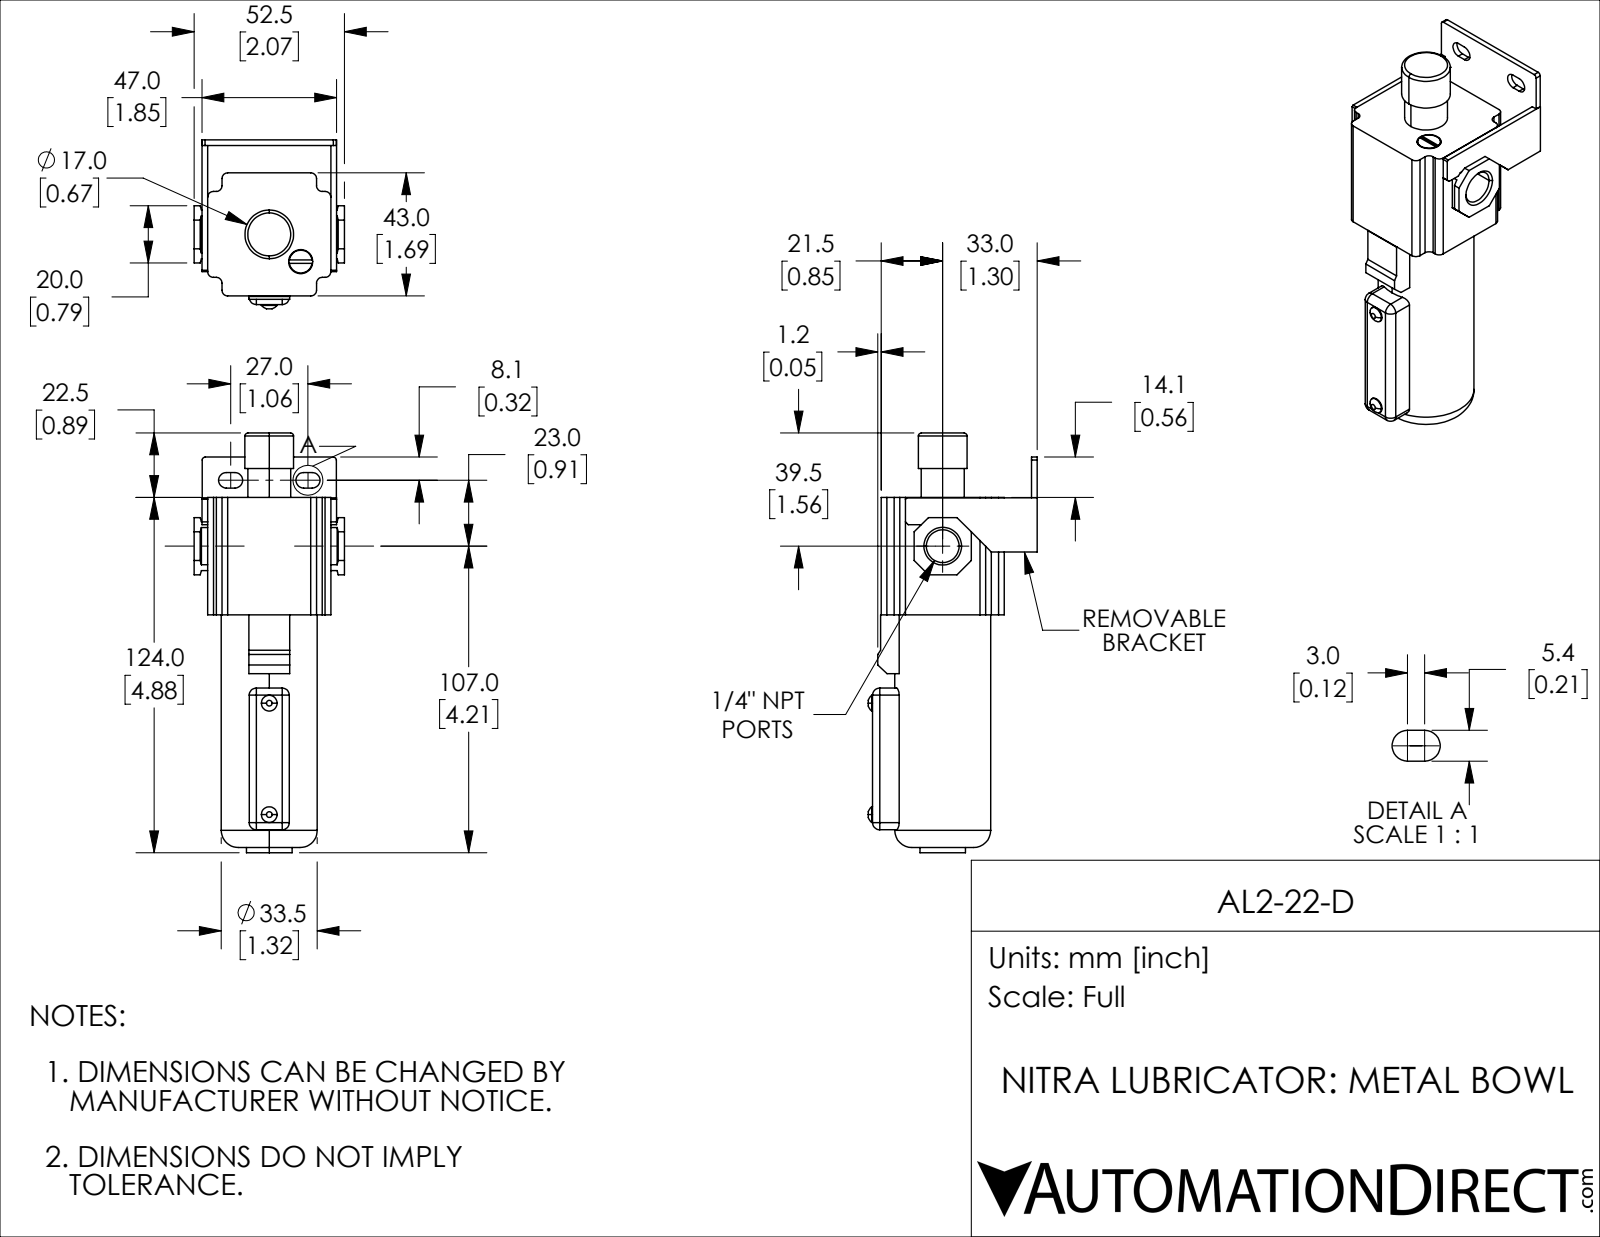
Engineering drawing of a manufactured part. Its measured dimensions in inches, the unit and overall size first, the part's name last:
Units: inches
Overall size (bounding box): 5.768 × 2.323 × 2.067
Round holes (diameter × count): ⌀0.331 ×1, ⌀0.451 ×1
Round bosses / shafts (diameter × count): ⌀0.217 ×2, ⌀1.319 ×1, ⌀0.669 ×1, ⌀0.626 ×1, ⌀0.591 ×1, ⌀0.315 ×1
Partial cylindrical surfaces — rounded edges, fillets, slot ends (radius × count): R0.079 ×12, R0.098 ×8, R0.106 ×4, R0.039 ×2
Main face-to-face distances: 0.079, 1.693, 0.374, 2.067, 0.453, 2.146, 1.772, 1.614, 1.201, 0.571
Volume: 9.69 in³ · Surface area: 42.71 in²
Bodies: 1 solid, 164 faces (102 planar, 46 cylindrical, 16 other)
Part name (STEP PRODUCT): AL2-22-D
STEP written by: SolidWorks 2019 (CONFIG_CONTROL_DESIGN)
